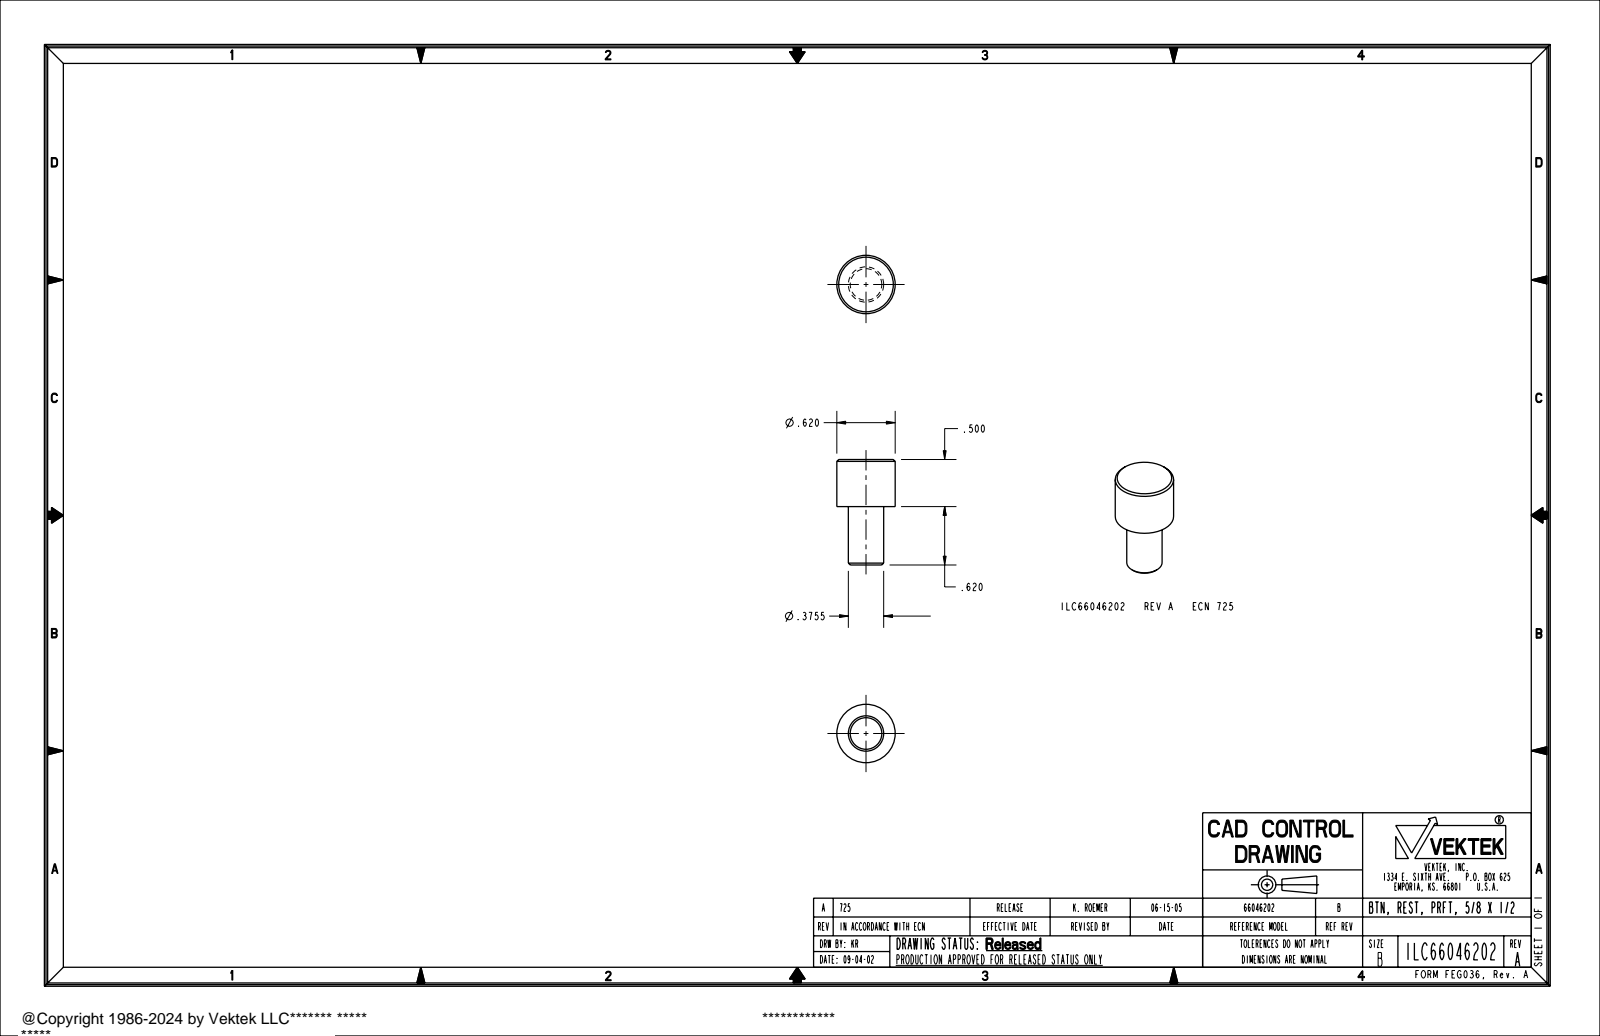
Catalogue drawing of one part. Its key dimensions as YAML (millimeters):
part_name: "ILC66046202"
step_written_by: "PRO/ENGINEER BY PARAMETRIC TECHNOLOGY CORPORATION, 2004290 (AUTOMOTIVE_DESIGN_CC2)"
units: millimeters
bodies: {solids: 1, faces: 11, planar: 3, cylindrical: 4, other: 4}
overall_size: [28.4, 15.7, 15.7]
volume: 3590
surface_area: 1465
round_bosses_or_shafts:
  - {diameter: 15.7, count: 1}
  - {diameter: 9.6, count: 1}
face_to_face_distances: [12.7, 15.7, 28.4]
